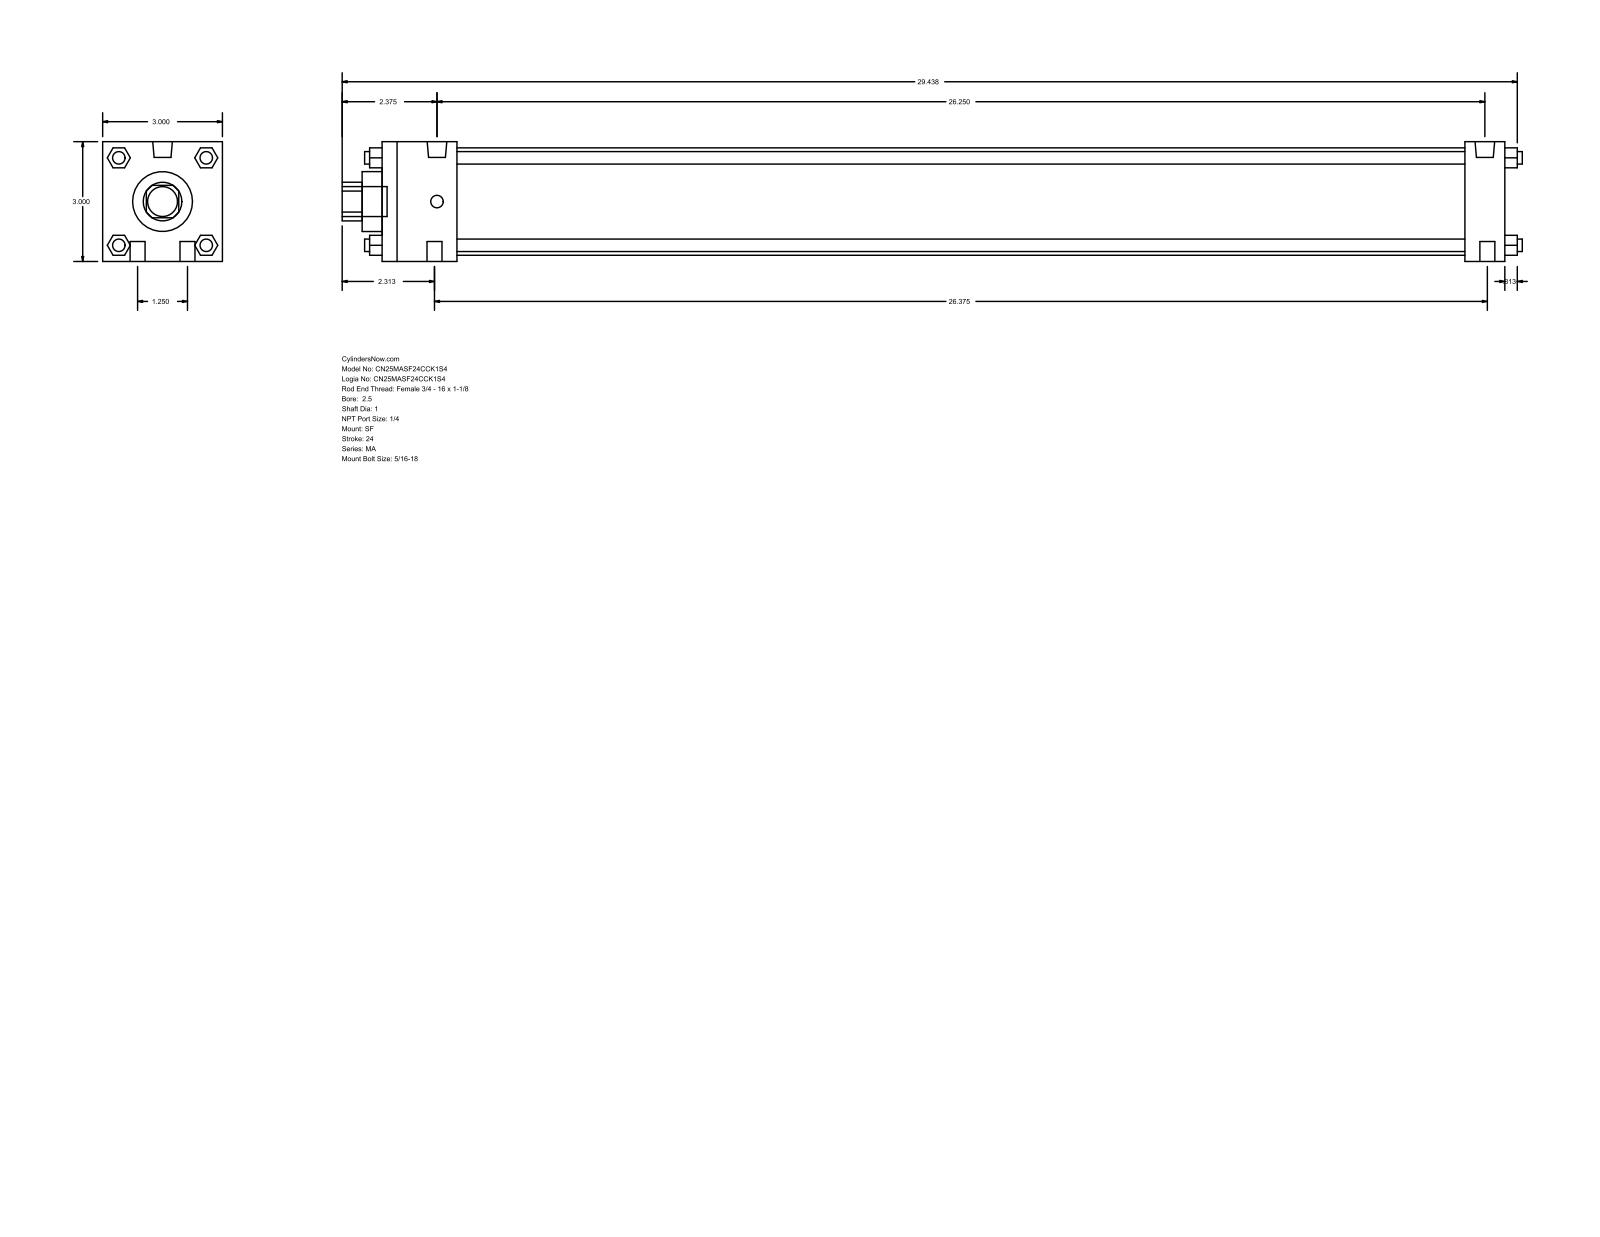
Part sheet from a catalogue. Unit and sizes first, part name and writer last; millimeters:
Units: millimetres
Overall size (bounding box): 750.89 × 76.2 × 76.2
Round holes (diameter × count): ⌀25.4 ×1, ⌀38.1 ×1, ⌀68.33 ×1
Round bosses / shafts (diameter × count): ⌀7.94 ×6, ⌀9.53 ×4, ⌀12.49 ×2, ⌀19.05 ×1
Partial cylindrical surfaces — rounded edges, fillets, slot ends (radius × count): R12.29 ×1
Main face-to-face distances: 76.2, 714.37, 12.7, 688.98, 25.39, 47.63, 641.35, 666.74, 27.81, 48.17
Bodies: 0 solids, 124 faces (94 planar, 30 cylindrical, 0 other)
Part name (STEP PRODUCT): MA_SF__0250_1
STEP written by: GSSL Pune (CONFIG_CONTROL_DESIGN)
